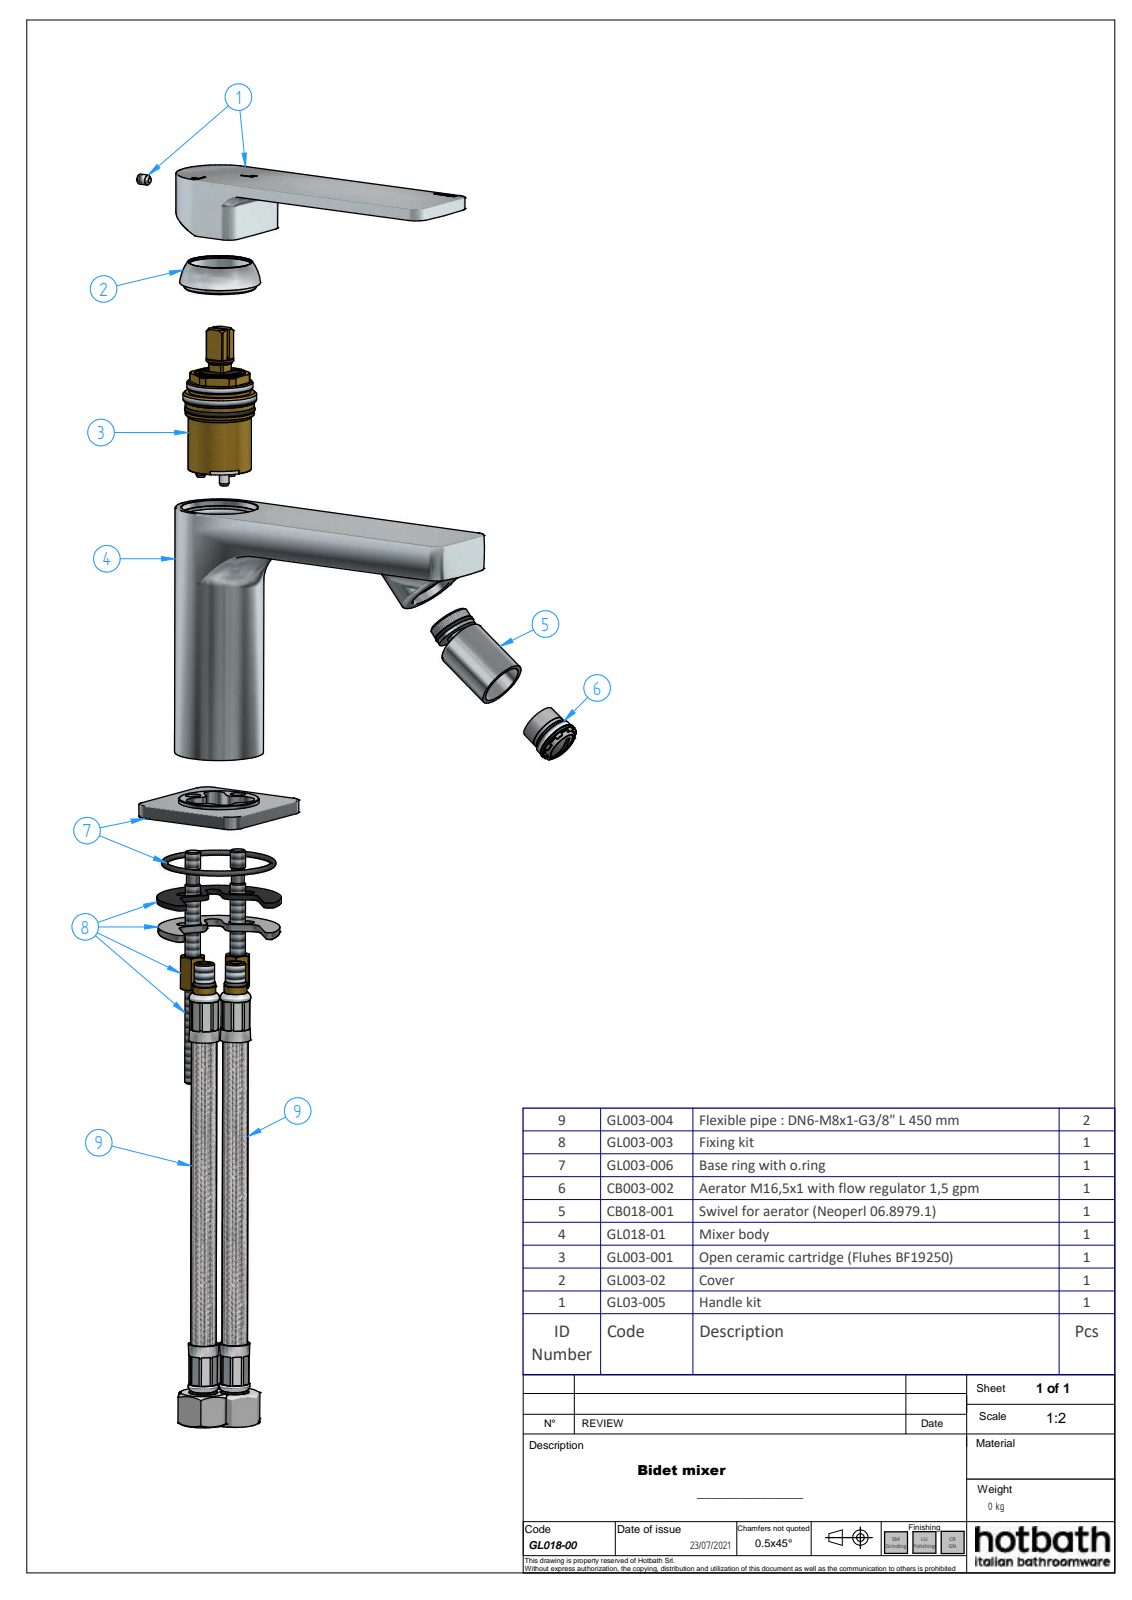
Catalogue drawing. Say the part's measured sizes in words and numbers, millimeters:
The part is named "GL018-00; GL003-02; GL003-05; CB003-002 (+8 more)". Its 3-D file was written by "ST-DEVELOPER v16.7 (AUTOMOTIVE_DESIGN)". It is 11 solids with 829 faces: 220 planar, 169 cylindrical and 440 other. Overall it measures 152.94 by 127.58 by 48 millimeters. Its volume is 104 183 cubic millimeters and its surface area 70 243 square millimeters. Round holes: 4 of diameter 4, 2 of diameter 4.92, 2 of diameter 5.5, 2 of diameter 6, 2 of diameter 6.92, 2 of diameter 9, 2 of diameter 12, 1 of diameter 3.24, 1 of diameter 4.2, 1 of diameter 10, 1 of diameter 11.03, 1 of diameter 12.2. Round bosses or shafts: 2 of diameter 16.5, 1 of diameter 35, 1 of diameter 31.7, 1 of diameter 28.5, 1 of diameter 20, 1 of diameter 15.23, 1 of diameter 15.22, 1 of diameter 15.03. Partial cylindrical surfaces (rounded edges, fillets, slot ends): 13 of radius 0.5, 11 of radius 5, 10 of radius 1, 10 of radius 2, 9 of radius 3, 8 of radius 0.2, 4 of radius 2.5, 3 of radius 6.5. The main face-to-face distances are 1.5, 3.5, 5, 7, 68.6, 67.1, 63.6, 48, 5.5, 19.9. The hole center spacings are 1.57, 3.18, 6.21, 7.16, 8.04, 9.37, 10.4, 11.01.
